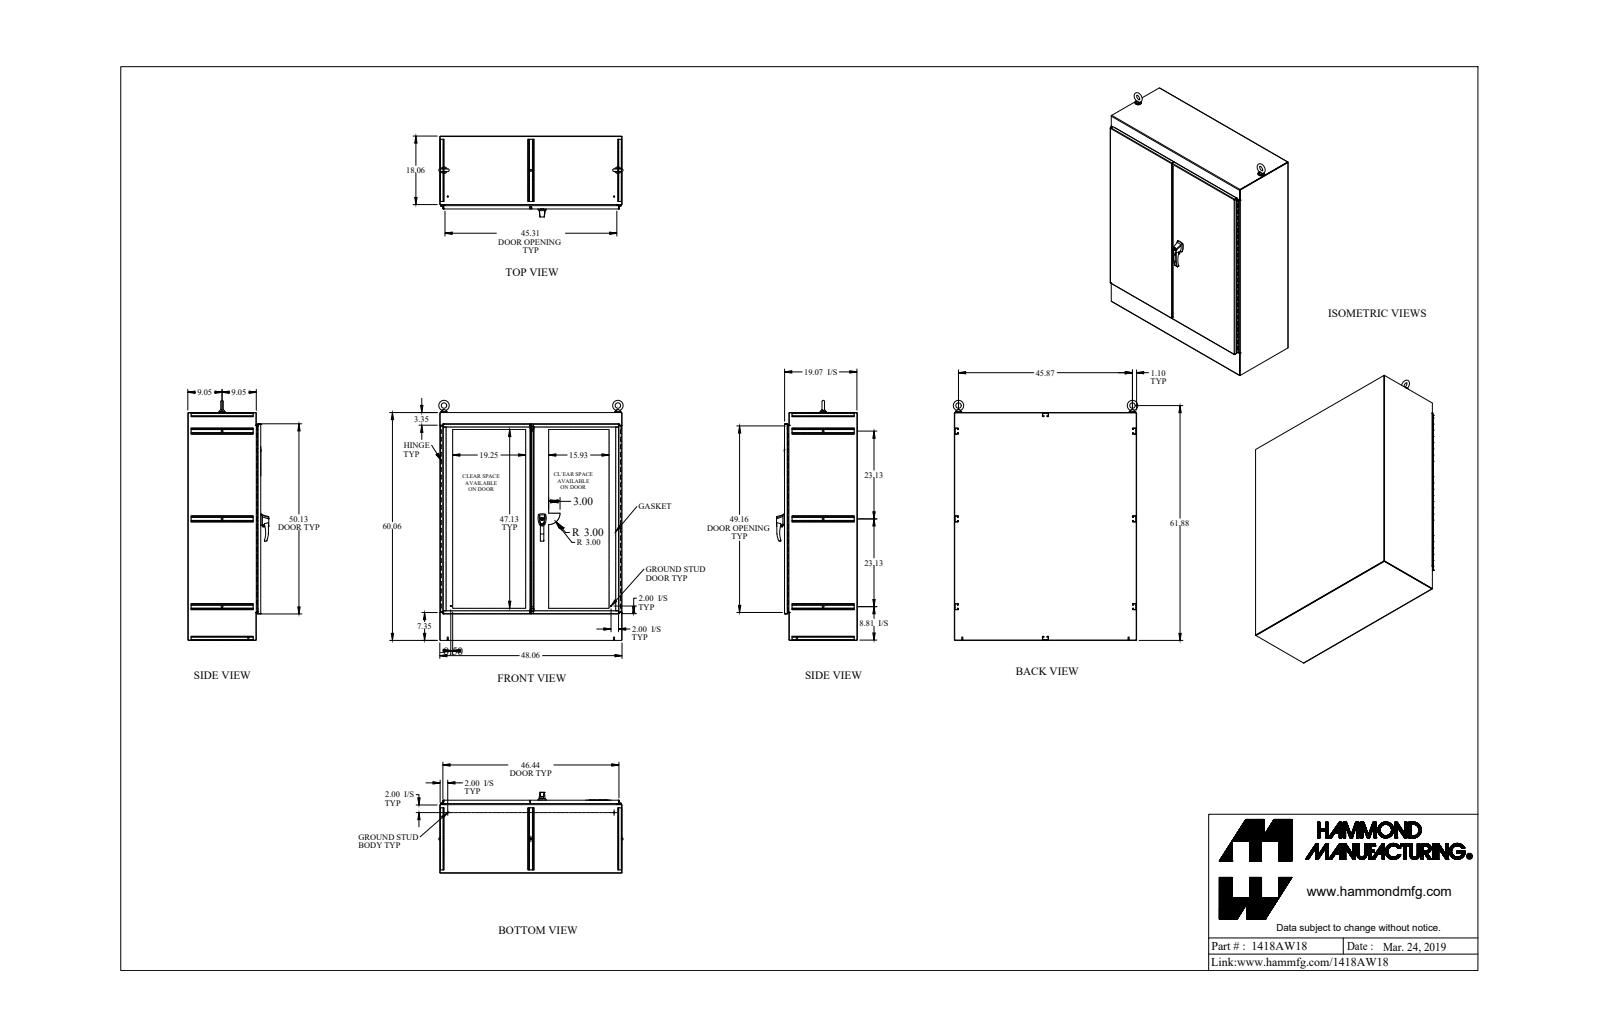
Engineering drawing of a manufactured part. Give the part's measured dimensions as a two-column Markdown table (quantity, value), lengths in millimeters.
| quantity | value |
| --- | --- |
| part name | 1418AW18 |
| STEP written by | SolidWorks 2019 (AUTOMOTIVE_DESIGN) |
| units | millimeters |
| bodies | 74 solids, 2575 faces (1490 planar, 946 cylindrical, 139 other) |
| overall size | 1618.3 × 1247.6 × 542 |
| volume | 19 500 000 mm³ |
| surface area | 15 620 000 mm² |
| round holes (diameter × count) | 7.7 × 18, 8.9 × 7, 12.7 × 4, 6.4 × 3, 2.8 × 2, 6.5 × 2, 7.1 × 2, 7.1 × 2, 8 × 2, 9.9 × 2, 10.5 × 2, 13.4 × 2 |
| round bosses / shafts (diameter × count) | 7.1 × 6, 6.4 × 4, 44.5 × 2, 38.1 × 2, 31.8 × 2, 25.4 × 2, 19.1 × 2, 18.7 × 2 |
| partial cylindrical surfaces (radius × count) | 1.1 × 54, 3.5 × 48, 12.7 × 25, 3.2 × 22, 0.5 × 16, 1.5 × 15, 1.2 × 8, 1.3 × 8 |
| main face-to-face distances | 2.4, 3.2, 1.8, 485.1, 488.2, 483.2, 486.4, 1218.3, 1523.1, 1215.9 |
| hole center spacings | 152.4, 1186.6, 304.8, 1215.6, 457.2, 1262.4, 609.6, 1325.3 |
